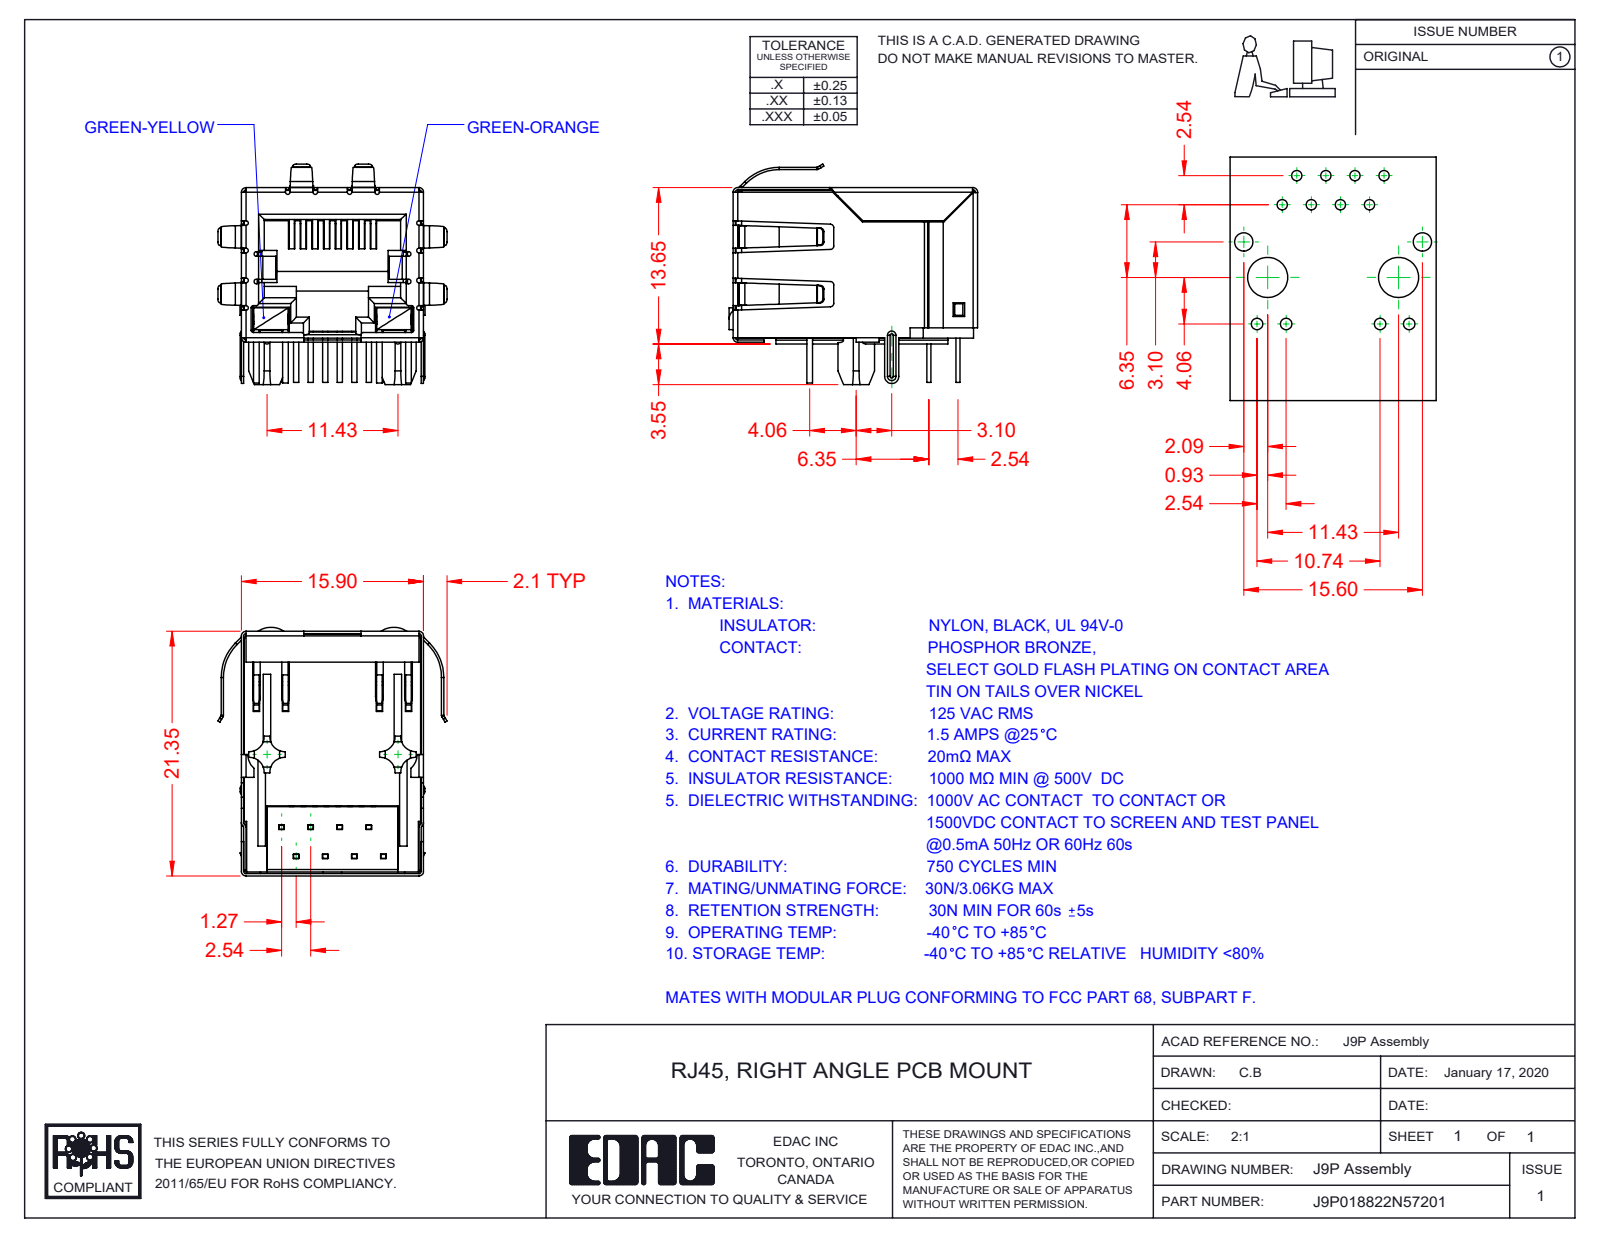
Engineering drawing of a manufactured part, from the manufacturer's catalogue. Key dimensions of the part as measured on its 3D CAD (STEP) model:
Part name (STEP PRODUCT): 9P-LED Assembly; 9P-LED Contacts; 9P-LED Contact Lock; 9P-LED Shield (+4 more)
STEP written by: SolidWorks 2016 (CONFIG_CONTROL_DESIGN)
Units: millimetres
Bodies: 13 solids, 1476 faces (1042 planar, 340 cylindrical, 94 other)
Overall size (bounding box): 21.7 × 20 × 19.25
Volume: 2 687 mm³ · Surface area: 7 515 mm²
Partial cylindrical surfaces — rounded edges, fillets, slot ends (radius × count): R0.2 ×39, R0.5 ×22, R0.3 ×20, R0.4 ×16, R1.3 ×8, R0.23 ×5, R0.11 ×4, R0.31 ×4
Main face-to-face distances: 15.45, 15.7, 15.65, 0.35, 0.54, 15.5, 12.36, 0.6, 1.4, 0.59
